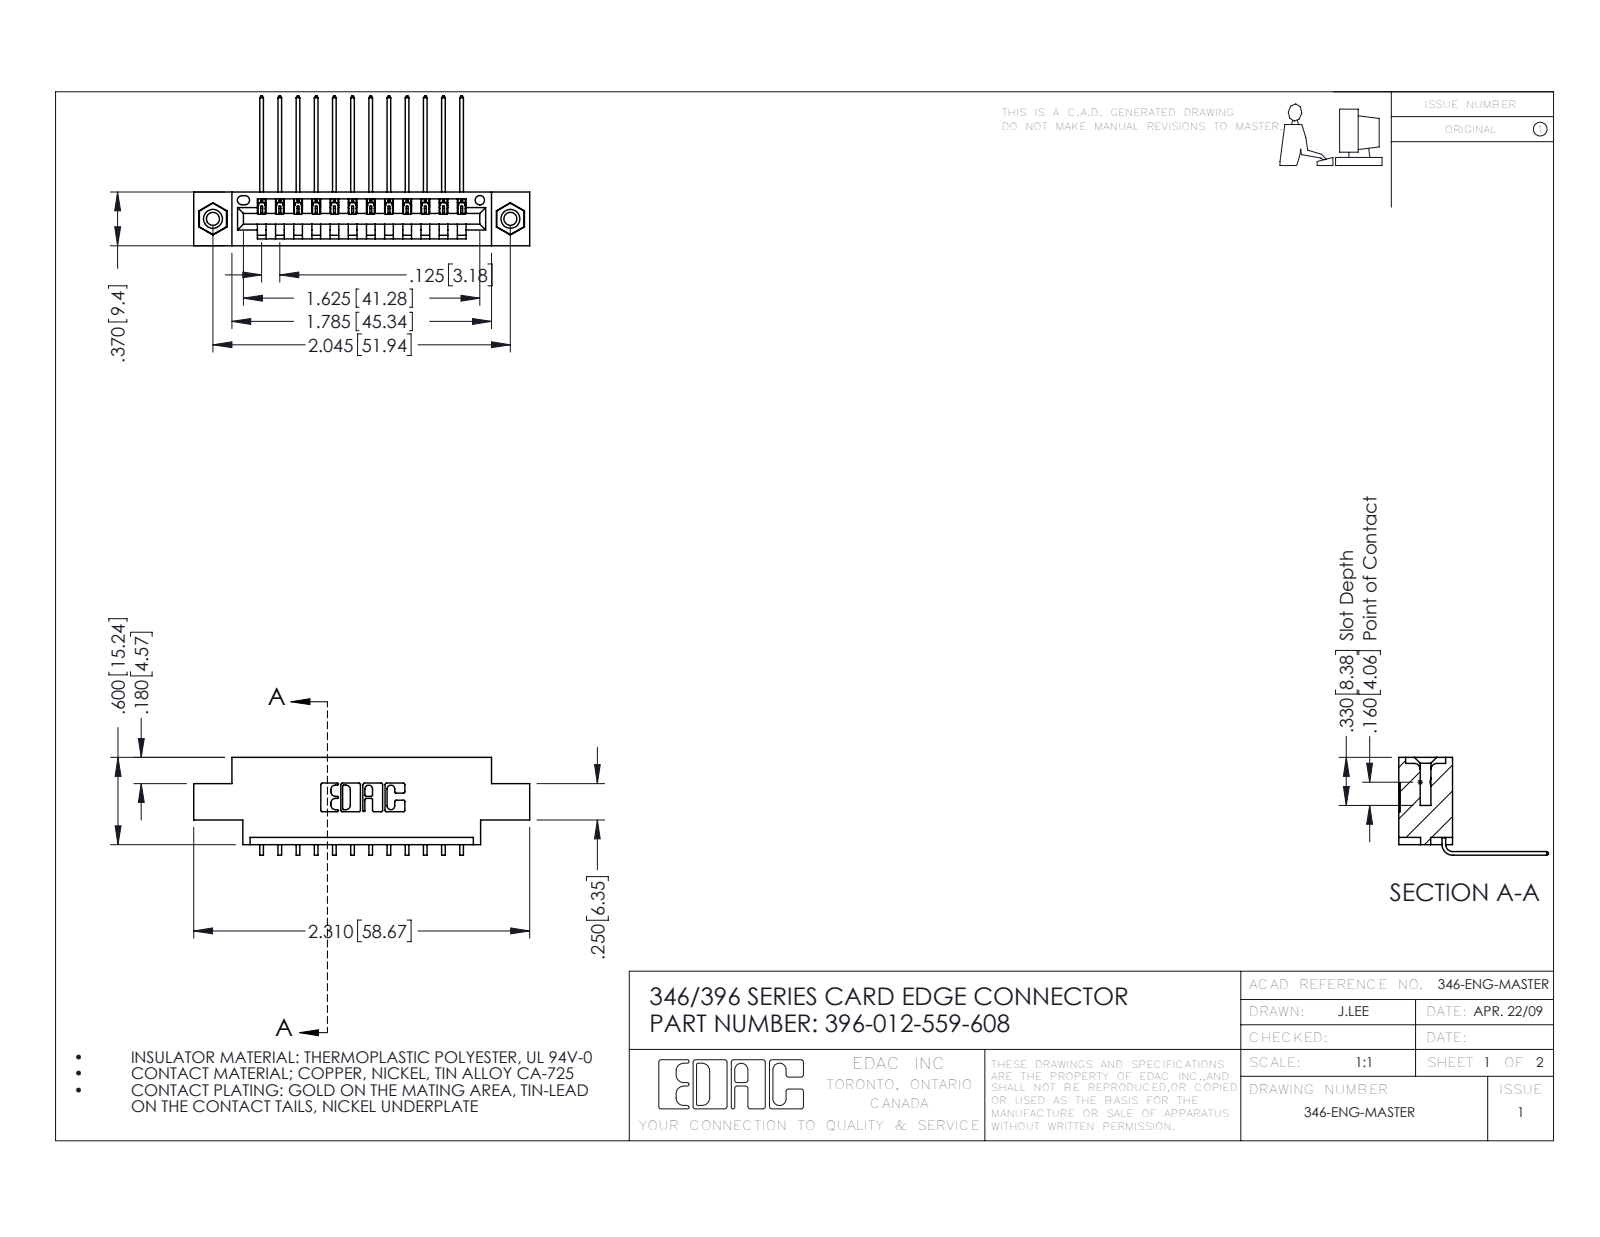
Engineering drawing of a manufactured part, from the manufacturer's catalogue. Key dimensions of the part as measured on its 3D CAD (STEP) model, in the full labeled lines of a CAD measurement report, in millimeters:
Part name (STEP PRODUCT): 396-012-559-608; 345-292-001_558 559 Tail - 1; 345-250-001_345-250-003-102; 346 Part_0.170 Offset - 0.156 Dia-TI
STEP written by: SolidWorks 2016 (CONFIG_CONTROL_DESIGN)
Units: millimetres
Bodies: 15 solids, 906 faces (616 planar, 274 cylindrical, 16 other)
Overall size (bounding box): 58.7 × 26.2 × 17.1
Volume: 5 290 mm³ · Surface area: 6 710 mm²
Round holes (diameter × count): ⌀2.3 ×2, ⌀3.2 ×2, ⌀4 ×2, ⌀1.6 ×1
Round bosses / shafts (diameter × count): ⌀3.9 ×2
Partial cylindrical surfaces — rounded edges, fillets, slot ends (radius × count): R0.2 ×24, R0.3 ×22, R0.2 ×6, R0.8 ×6, R0.7 ×3, R0.8 ×2, R1 ×2, R0.4 ×1
Main face-to-face distances: 1.2, 9.4, 6.4, 8.2, 0.6, 1.8, 5.6, 3.8, 2.5, 4.4
Hole centre spacings: 6.2, 46.7, 51.9
